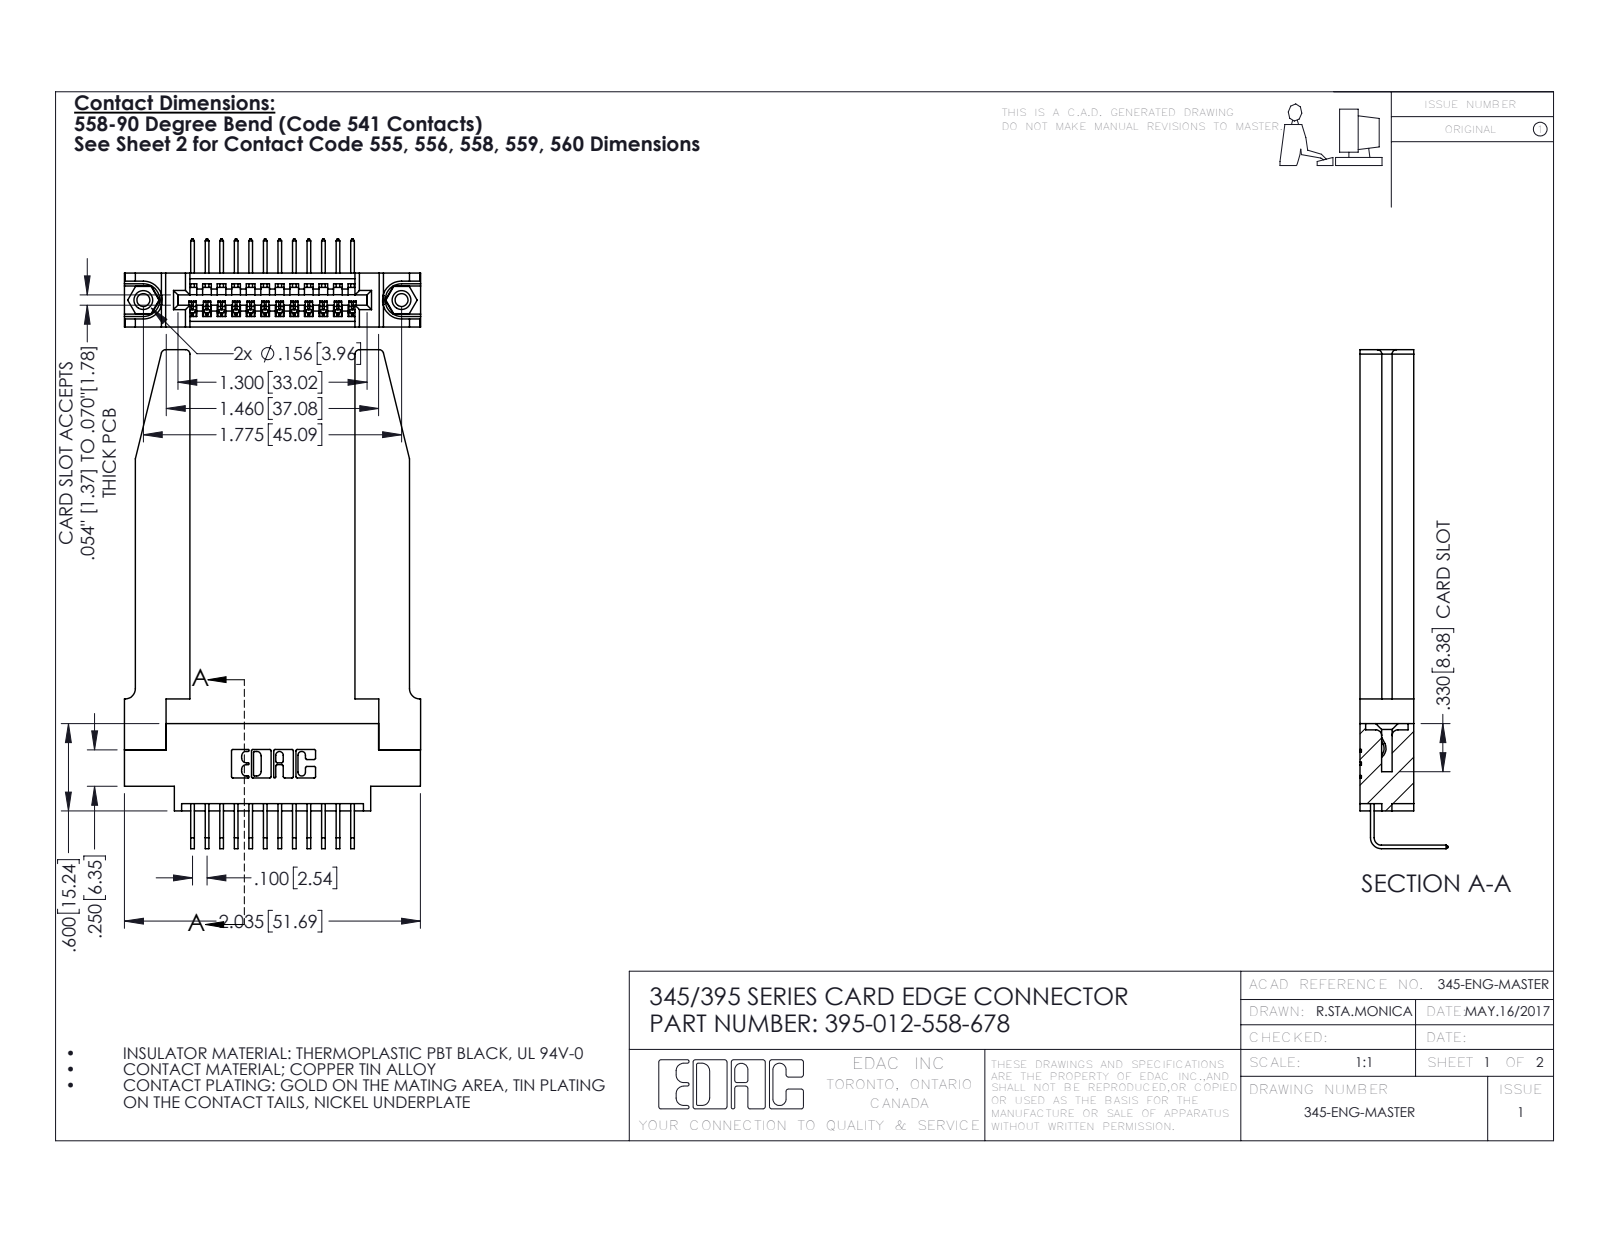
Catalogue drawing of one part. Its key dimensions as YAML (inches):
part_name: "395-012-558-678; 345-220-078_345-220-078; 345-250-001_345-250-001-102; 345 Part_0.170 Offset - 0.156 Dia-TH (+1 more)"
step_written_by: "SolidWorks 2016 (CONFIG_CONTROL_DESIGN)"
units: inches
bodies: {solids: 17, faces: 1084, planar: 730, cylindrical: 302, other: 52}
overall_size: [3.429, 2.036, 0.605]
volume: 0.754
surface_area: 20
round_holes:
  - {diameter: 0.089, count: 2}
  - {diameter: 0.125, count: 2}
  - {diameter: 0.156, count: 2}
  - {diameter: 0.064, count: 1}
round_bosses_or_shafts:
  - {diameter: 0.155, count: 2}
partial_cylinders:
  - {radius: 0.006, count: 24}
  - {radius: 0.01, count: 22}
  - {radius: 0.03, count: 8}
  - {radius: 0.007, count: 6}
  - {radius: 0.031, count: 6}
  - {radius: 0.026, count: 3}
  - {radius: 0.031, count: 2}
  - {radius: 0.04, count: 2}
face_to_face_distances: [0.37, 0.072, 0.298, 0.15, 0.148, 0.22, 0.077, 1.135, 0.2, 0.123]
hole_center_spacings: [0.27, 1.543, 1.775]
